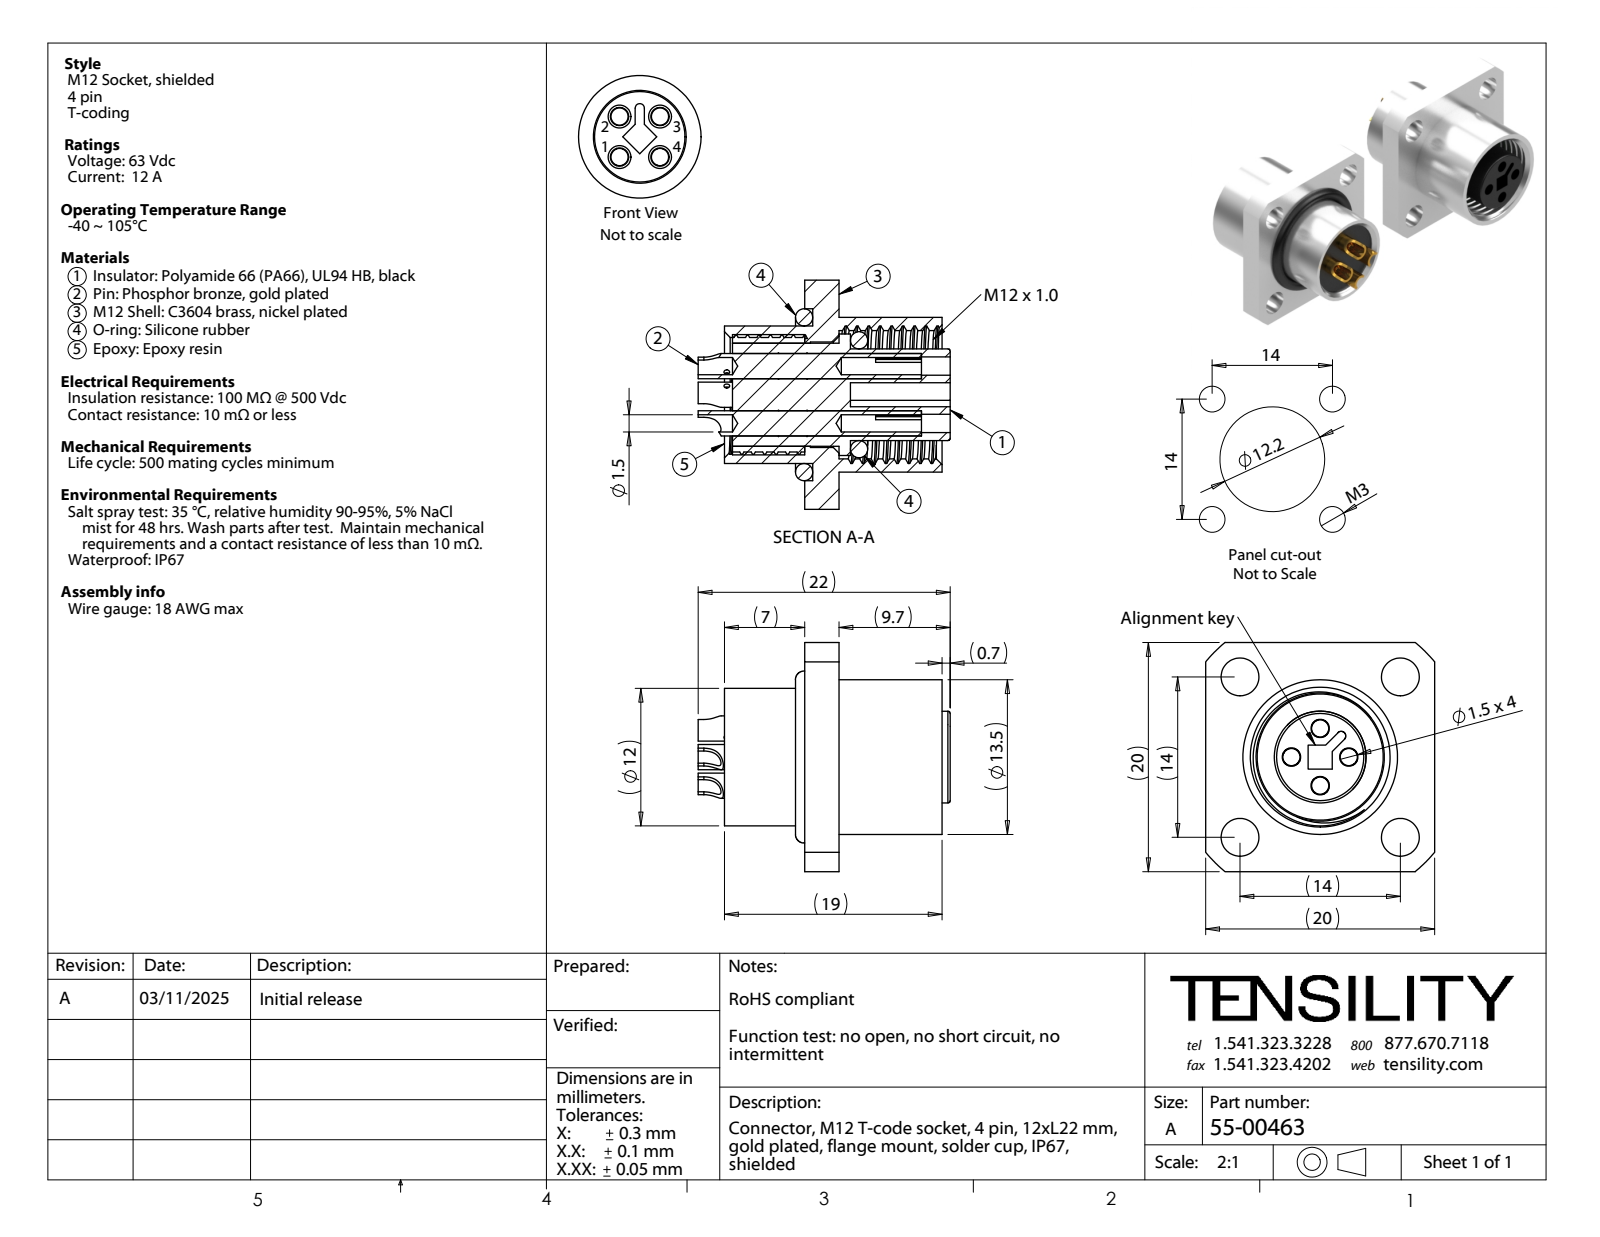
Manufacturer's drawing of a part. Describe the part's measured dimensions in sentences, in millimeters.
The part is named "55-00463-02; 55-00463-04; 55-00463-05; 55-00463 (+2 more)". Its 3-D file was written by "SolidWorks 2021 (CONFIG_CONTROL_DESIGN)". It is 9 solids with 274 faces: 83 planar, 134 cylindrical and 57 other. Overall it measures 22 by 20 by 20 millimeters. Its volume is 2 697 cubic millimeters and its surface area 5 218 square millimeters. Round holes: 4 of diameter 1.5, 4 of diameter 1.6, 4 of diameter 3.3, 2 of diameter 0.5, 1 of diameter 9, 1 of diameter 9.2, 1 of diameter 10, 1 of diameter 11.2, 1 of diameter 15. Round bosses or shafts: 4 of diameter 2.2, 1 of diameter 13.5, 1 of diameter 12, 1 of diameter 10.6, 1 of diameter 10.5, 1 of diameter 8. Partial cylindrical surfaces (rounded edges, fillets, slot ends): 2 of radius 1.86, 1 of radius 0.4, 1 of radius 13. The main face-to-face distances are 3, 0.7, 20, 7, 9.3, 6.3, 2.3, 11.05, 8.95, 12. The hole center spacings are 8.32, 11.8, 3.54, 2.5, 9.9, 14, 5, 19.8.
